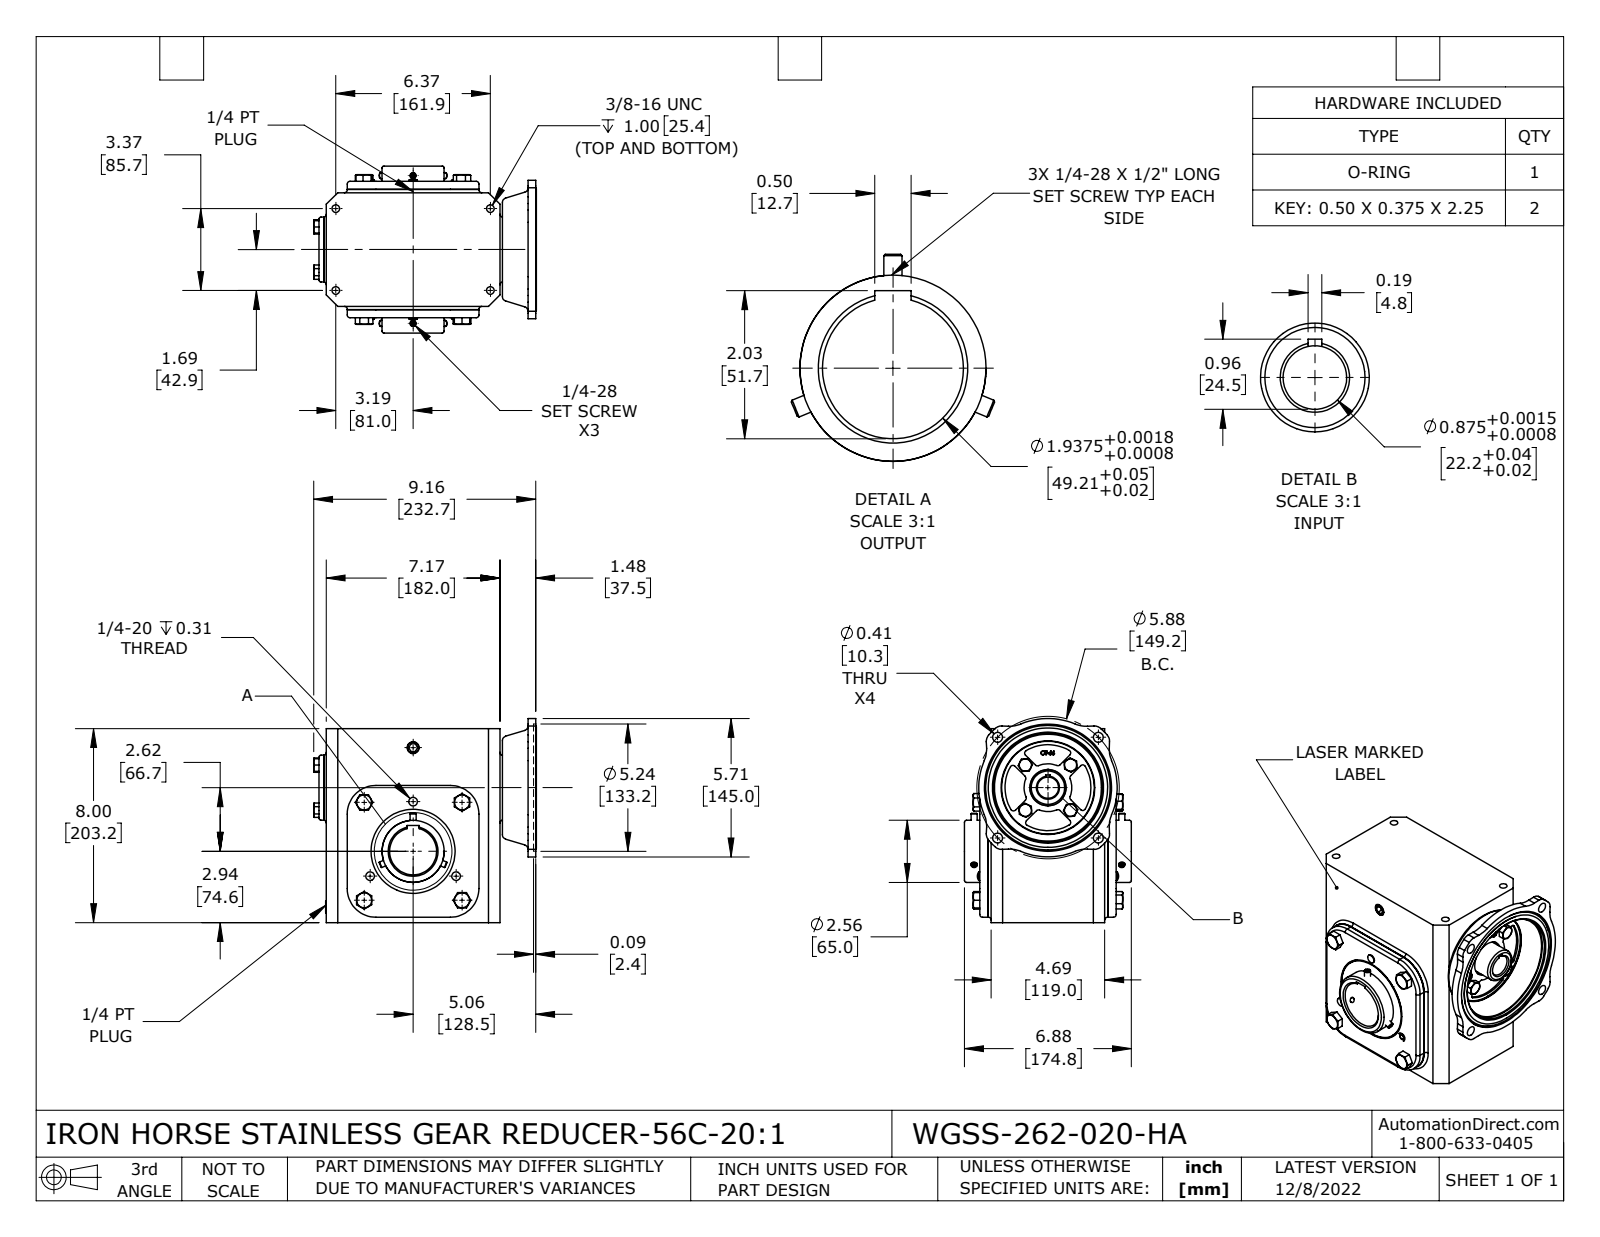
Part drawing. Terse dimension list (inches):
name: WGSS-262-020-HA
written by: SolidWorks 2021 (CONFIG_CONTROL_DESIGN)
unit: in
bodies: 45 solids, 1776 faces (625 planar, 516 cylindrical, 635 other)
size: 9.184 × 8.417 × 6.882
volume: 121.8 in³; area: 1 055 in²
holes: 6× ⌀0.213, 4× ⌀0.268, 4× ⌀0.313, 4× ⌀0.335, 4× ⌀0.354, 4× ⌀0.406, 4× ⌀0.433, 3× ⌀0.201, 2× ⌀0.079, 1× ⌀0.875, 1× ⌀0.941, 1× ⌀1.102
bosses: 6× ⌀0.25, 4× ⌀0.709, 4× ⌀0.394, 4× ⌀0.315, 3× ⌀0.354, 3× ⌀0.205, 1× ⌀4.921, 1× ⌀4.409
rounds: 40× R0.118, 12× R0.394, 12× R1.181, 8× R0.039, 8× R0.197, 6× R0.079, 4× R0.236, 2× R0.019
face distances: 0.197, 0.335, 4.961, 0.669, 7.803, 0.472, 5.157, 4.488, 0.138, 6.969
hole spacings: 3.22, 1.319, 1.619, 1.865, 2.855, 2.937, 3.465, 4.037
